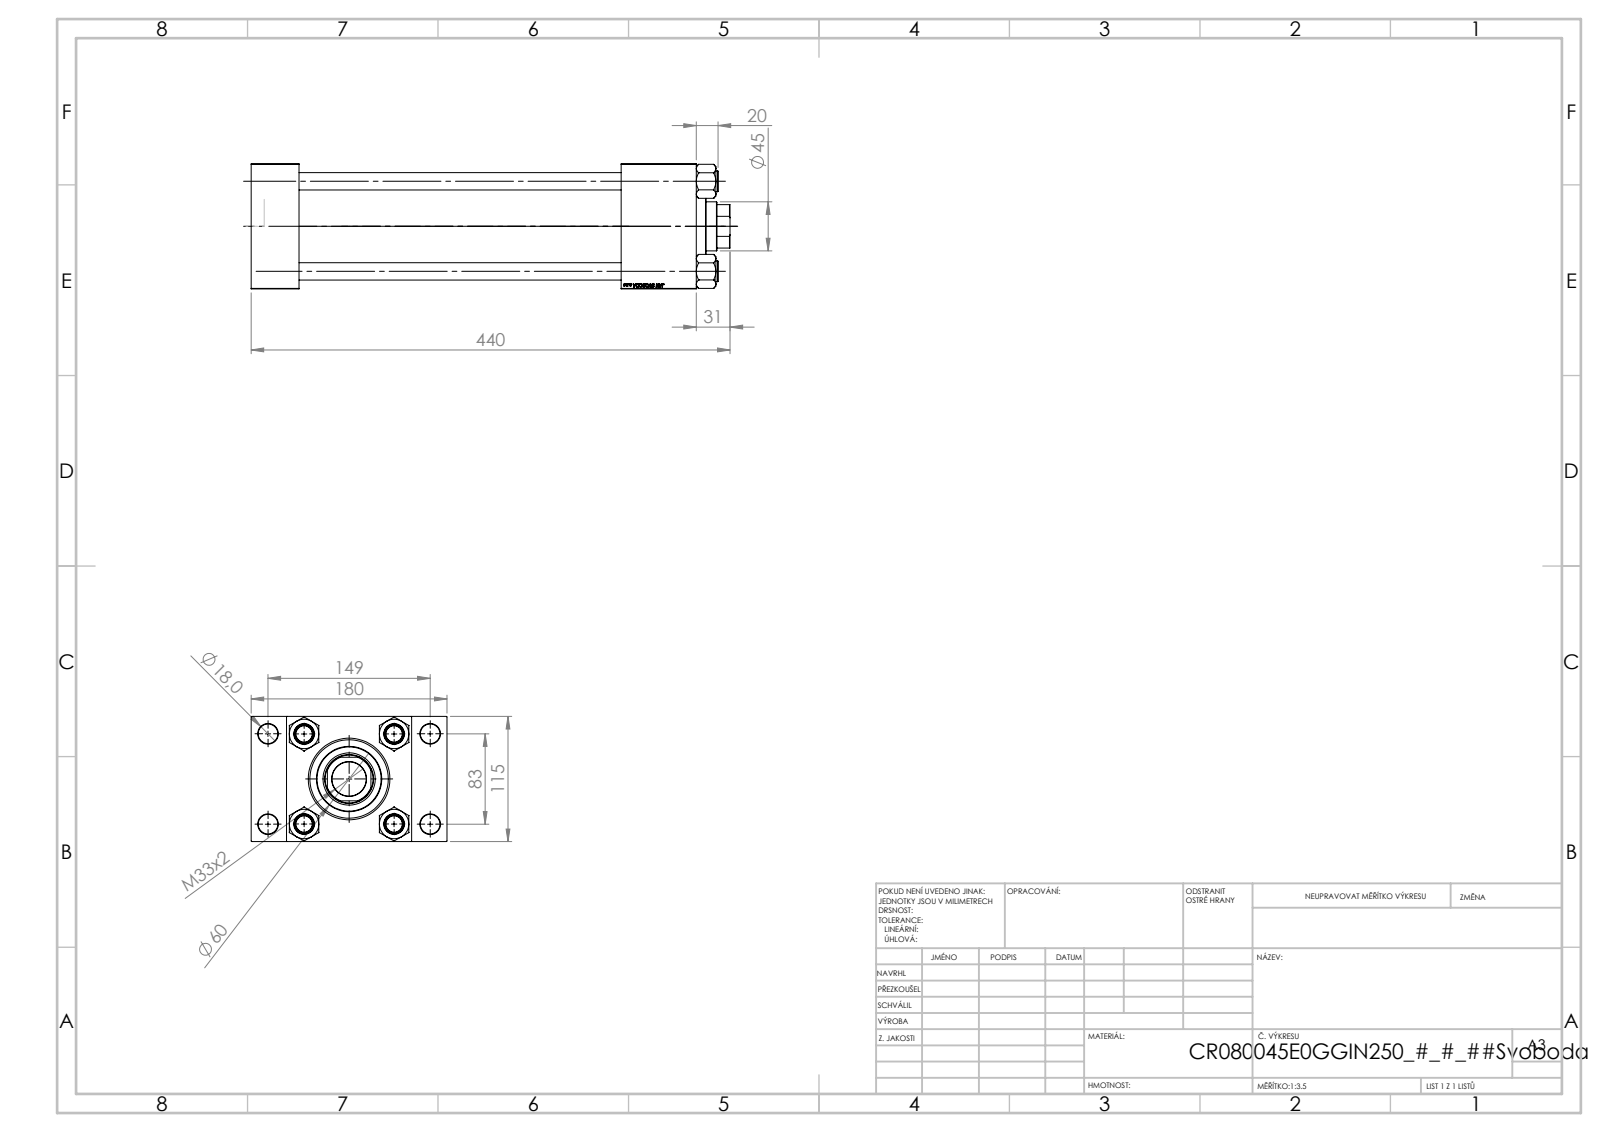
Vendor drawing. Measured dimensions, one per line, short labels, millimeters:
name: V215CR_E_Body; V215CR_TYCINKA_E; V215CR_VCP_E; NUT_M5_E (+1 more)
written by: SolidWorks 2019 (CONFIG_CONTROL_DESIGN)
unit: mm
bodies: 11 solids, 1185 faces (546 planar, 87 cylindrical, 552 other)
size: 440 × 180 × 115
volume: 2 849 000 mm³; area: 513 700 mm²
holes: 4× ⌀16, 4× ⌀18, 2× ⌀7, 2× ⌀26.44, 2× ⌀35, 1× ⌀31.5, 1× ⌀45, 1× ⌀48, 1× ⌀61, 1× ⌀72, 1× ⌀80
bosses: 4× ⌀19, 1× ⌀86, 1× ⌀60
rounds: 1× R22
face distances: 115, 44, 409, 365, 32.5, 147.5, 340, 296, 69, 180
hole spacings: 33.15, 58.48, 82.7, 85.28, 89.24, 115.85, 142.43, 83
